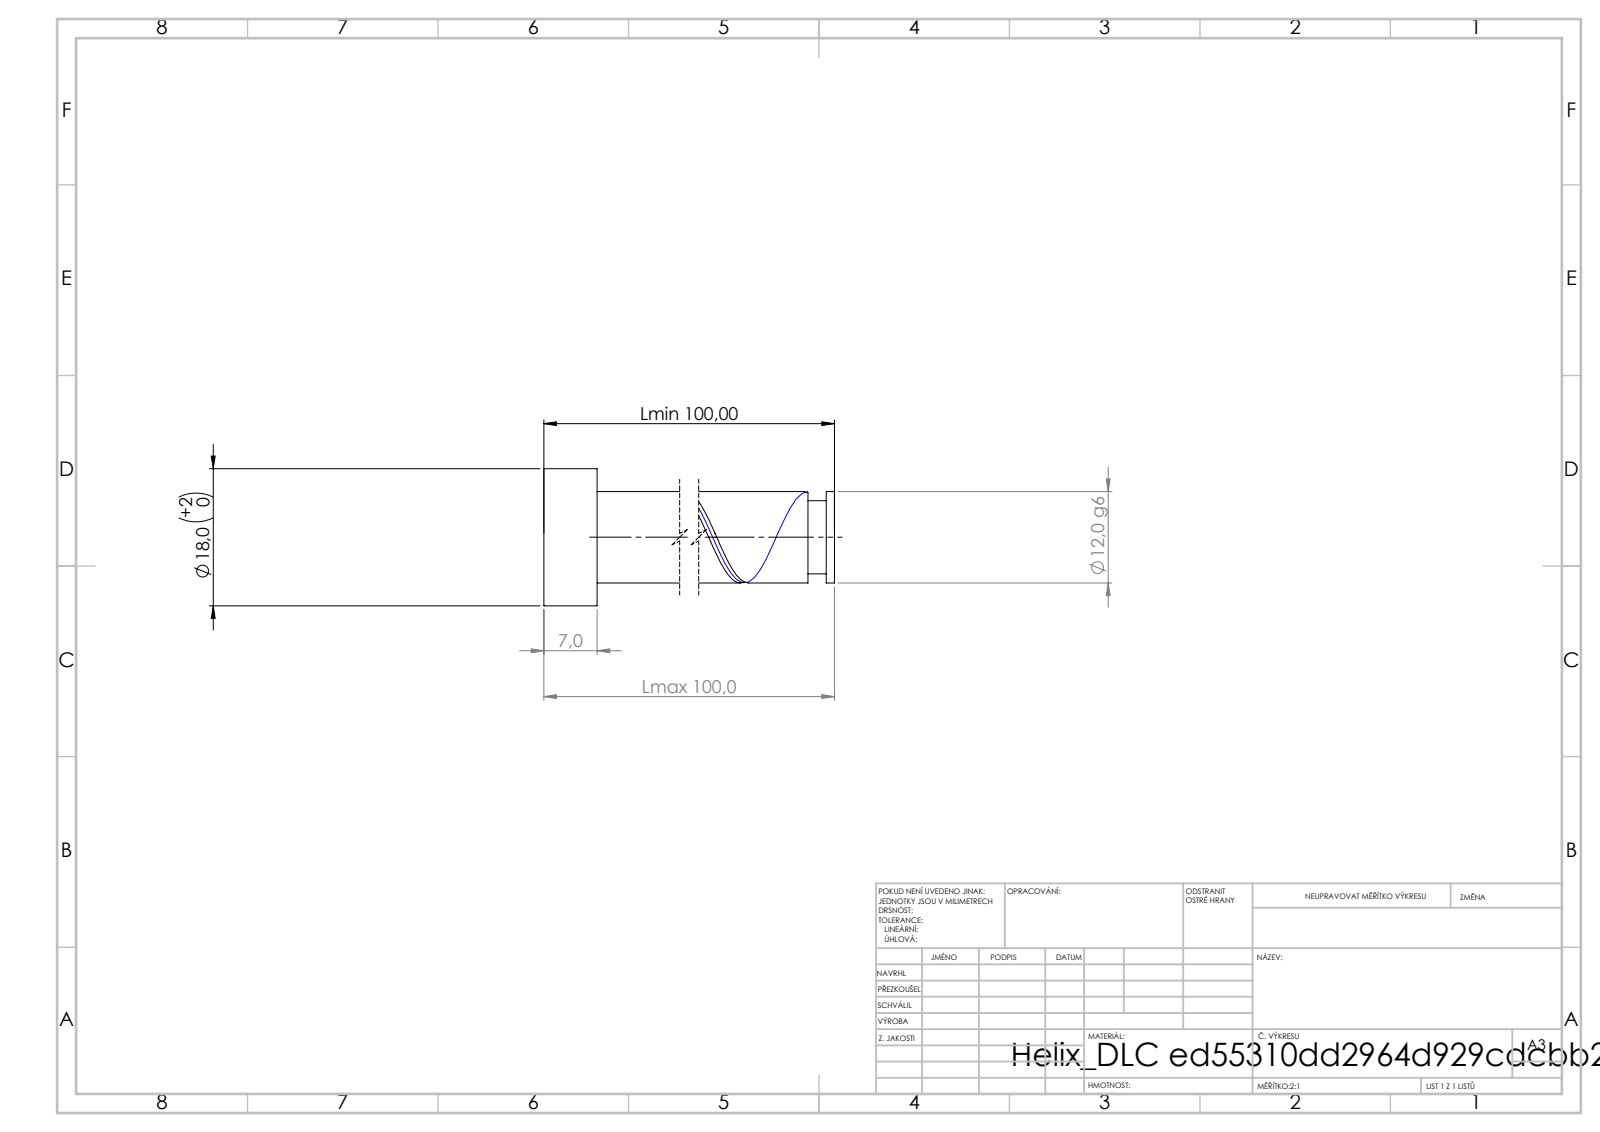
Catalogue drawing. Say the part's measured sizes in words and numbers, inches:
Its 3-D file was written by "SolidWorks 2019 (CONFIG_CONTROL_DESIGN)". It is 1 solid with 21 faces: 6 planar, 14 cylindrical and 1 other. Overall it measures 3.937 by 0.709 by 0.709 inches. Its volume is 0.738 cubic inches and its surface area 7.232 square inches. Round bosses or shafts: 1 of diameter 0.709, 1 of diameter 0.472, 1 of diameter 0.378. The main face-to-face distances are 0.276, 3.937, 3.661, 3.894, 3.619, 0.043, 3.8, 3.524, 0.094, 0.137.
